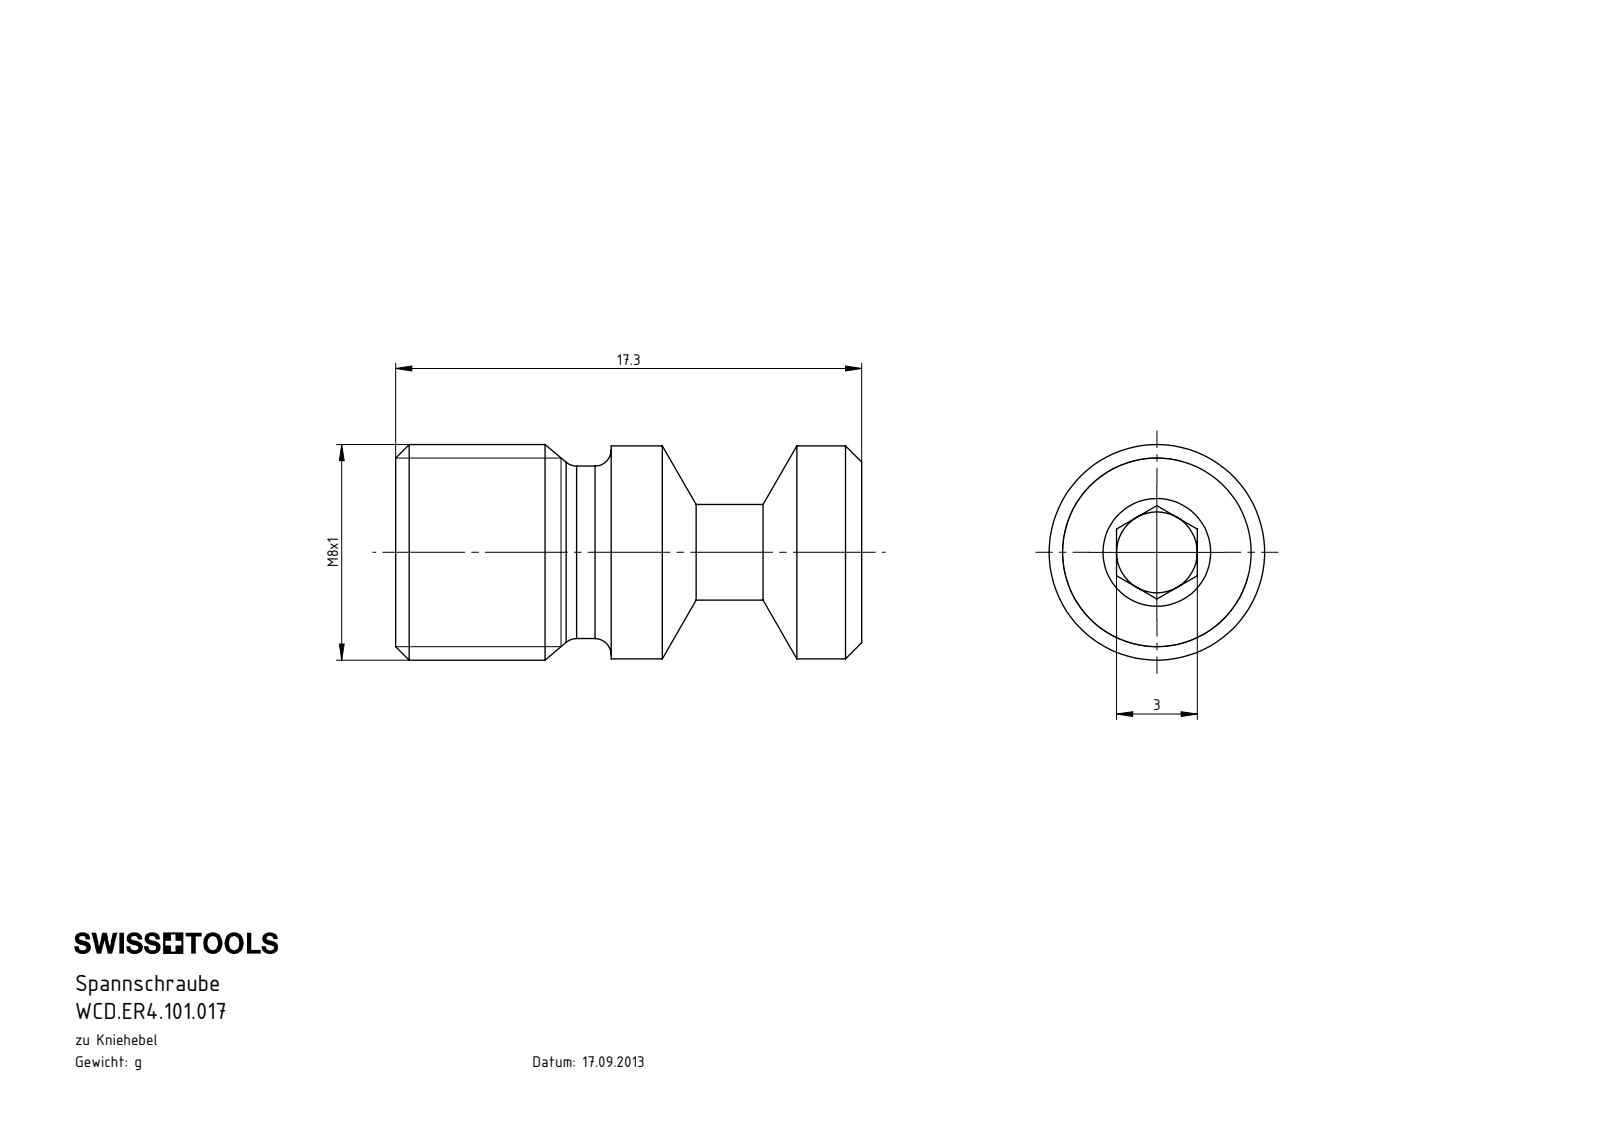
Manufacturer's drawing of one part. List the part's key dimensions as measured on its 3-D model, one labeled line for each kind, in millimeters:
Part name (STEP PRODUCT): WCD.ER4.101.017
STEP written by: SolidWorks 2017 (AUTOMOTIVE_DESIGN)
Units: millimetres
Bodies: 1 solid, 43 faces (15 planar, 10 cylindrical, 18 other)
Overall size (bounding box): 17.3 × 8 × 8
Volume: 630 mm³ · Surface area: 557 mm²
Round bosses / shafts (diameter × count): ⌀8 ×1, ⌀7.9 ×1, ⌀6.4 ×1, ⌀3.55 ×1
Main face-to-face distances: 17.3, 3, 8, 9.3, 4, 13.3
